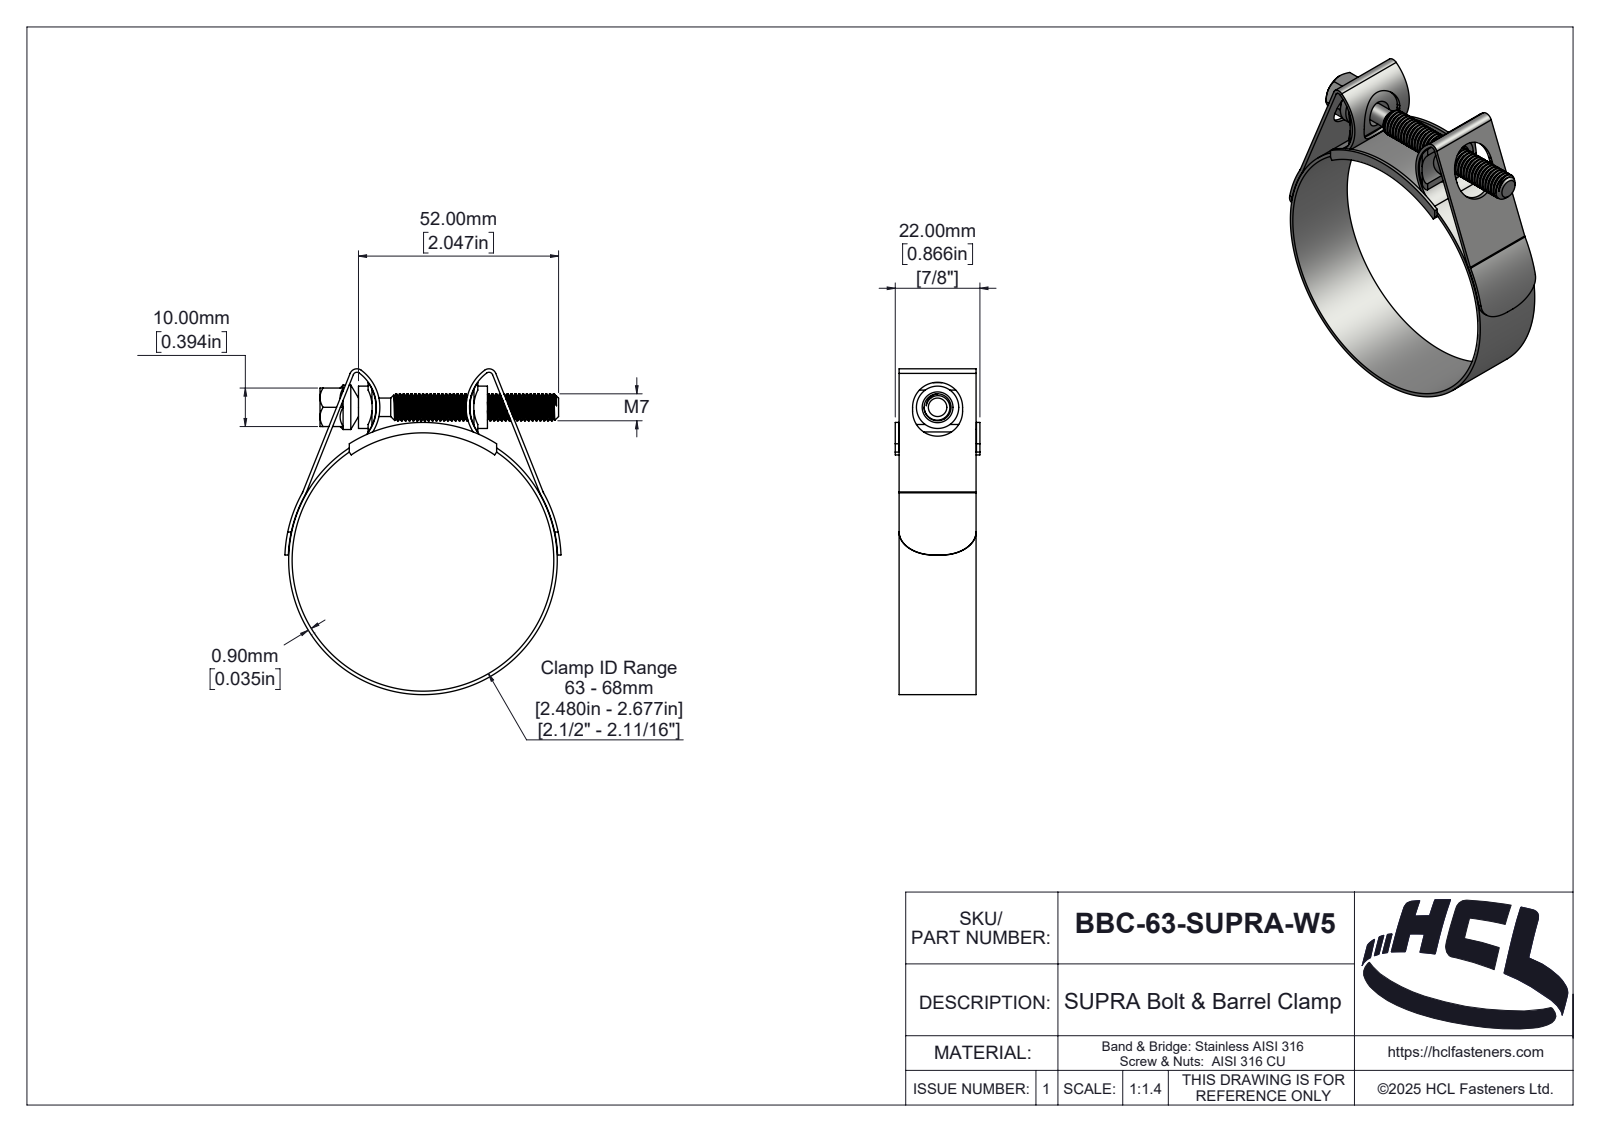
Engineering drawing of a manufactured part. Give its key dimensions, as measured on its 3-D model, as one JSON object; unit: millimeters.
{"part_name": "BBC-63-SUPRA-W5", "step_written_by": "SolidWorks 2025 (AUTOMOTIVE_DESIGN)", "units": "millimeters", "bodies": {"solids": 5, "faces": 325, "planar": 46, "cylindrical": 199, "other": 80}, "overall_size": [84.63, 71.75, 22], "volume_mm3": 9429, "surface_area_mm2": 18227, "round_holes": [[68, 1]], "round_bosses_or_shafts": [[69.8, 1], [11.55, 1], [11, 1], [7, 1], [4.8, 1]], "partial_cylinders_radius": [[1, 6], [1.9, 2], [2, 2], [2.9, 2], [6.5, 2], [10.02, 2], [11.02, 2], [11.12, 2]], "face_to_face_distances": [0.9, 20, 1, 21, 21.1, 20.1, 10, 22, 2.5, 31.02]}
